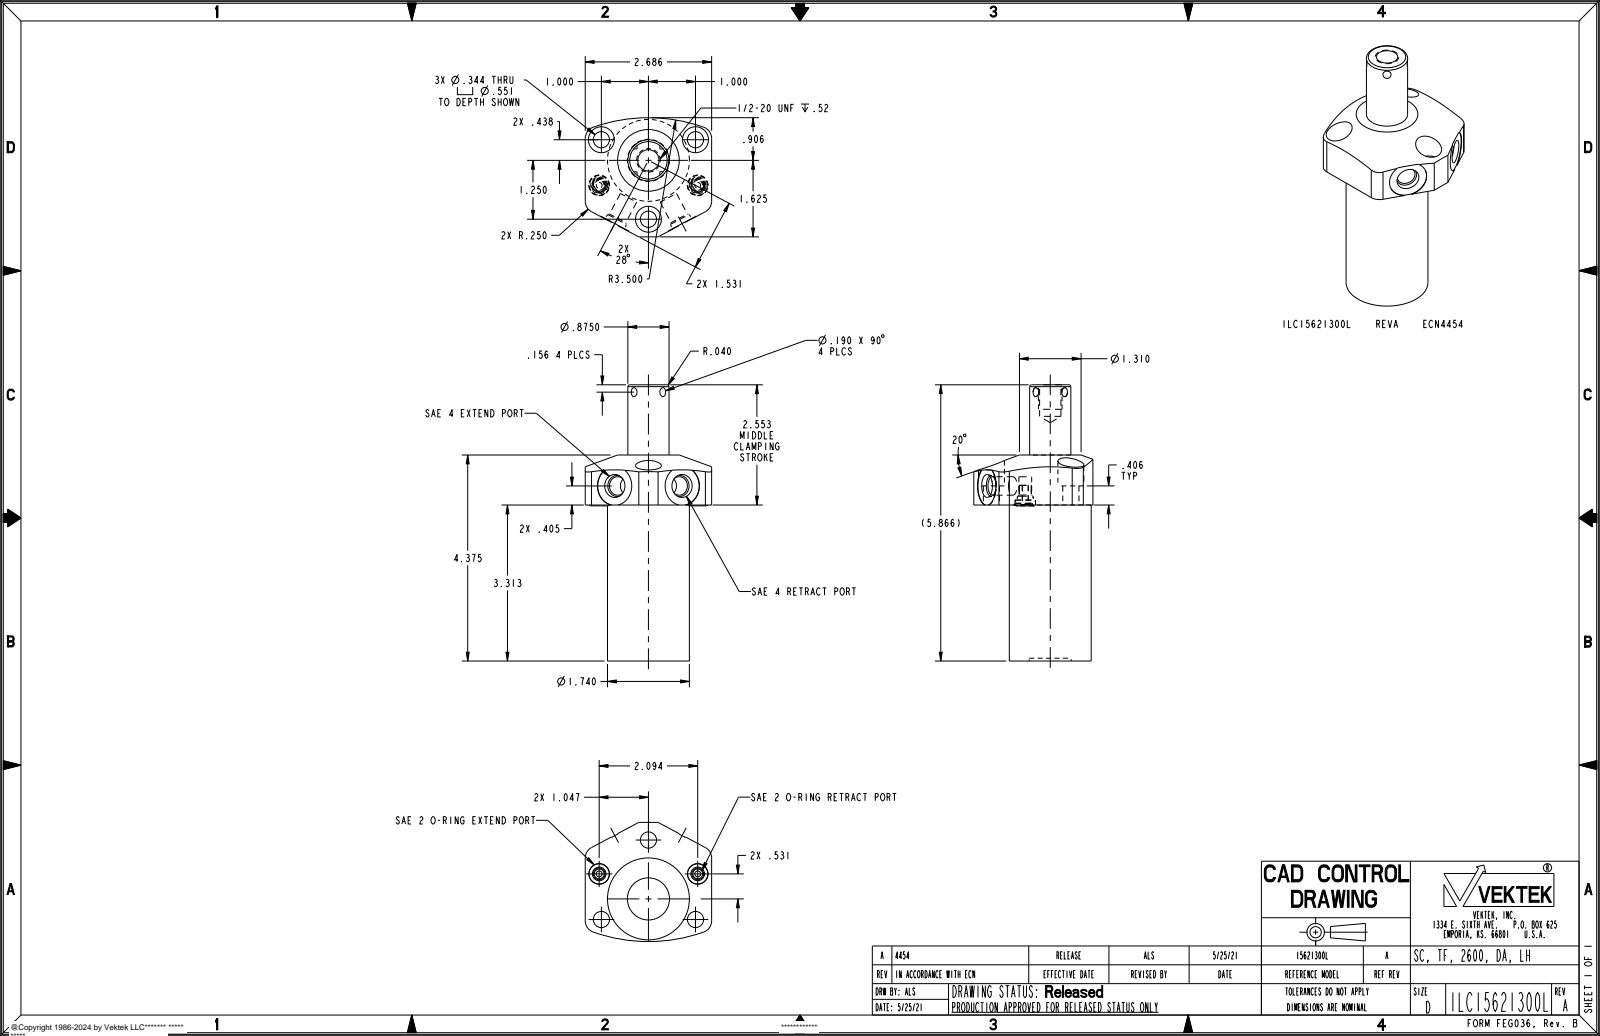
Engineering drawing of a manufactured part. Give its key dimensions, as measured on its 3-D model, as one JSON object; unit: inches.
{"part_name": "ILC15621300L", "step_written_by": "PRO/ENGINEER BY PARAMETRIC TECHNOLOGY CORPORATION, 2013320 (CONFIG_CONTROL_DESIGN)", "units": "inches", "bodies": {"solids": 1, "faces": 131, "planar": 34, "cylindrical": 59, "other": 38}, "overall_size": [5.866, 2.686, 2.531], "volume_in3": 13.44, "surface_area_in2": 50.7, "round_holes": [[0.344, 3], [0.551, 3], [0.125, 2], [0.272, 2], [0.392, 2], [0.438, 2], [0.453, 1], [0.895, 1]], "round_bosses_or_shafts": [[0.43, 2], [0.256, 2], [0.21, 2], [1.74, 1], [0.875, 1], [0.5, 1]], "partial_cylinders_radius": [[0.25, 4], [0.412, 2], [3.5, 1]], "face_to_face_distances": [3.313, 2.686, 4.375, 1.062, 0.06, 3.253, 4.315, 3.719, 3.659, 0.406], "hole_center_spacings": [0.97, 1.092, 1.174, 1.27, 1.962, 2.265, 1.25, 2]}
